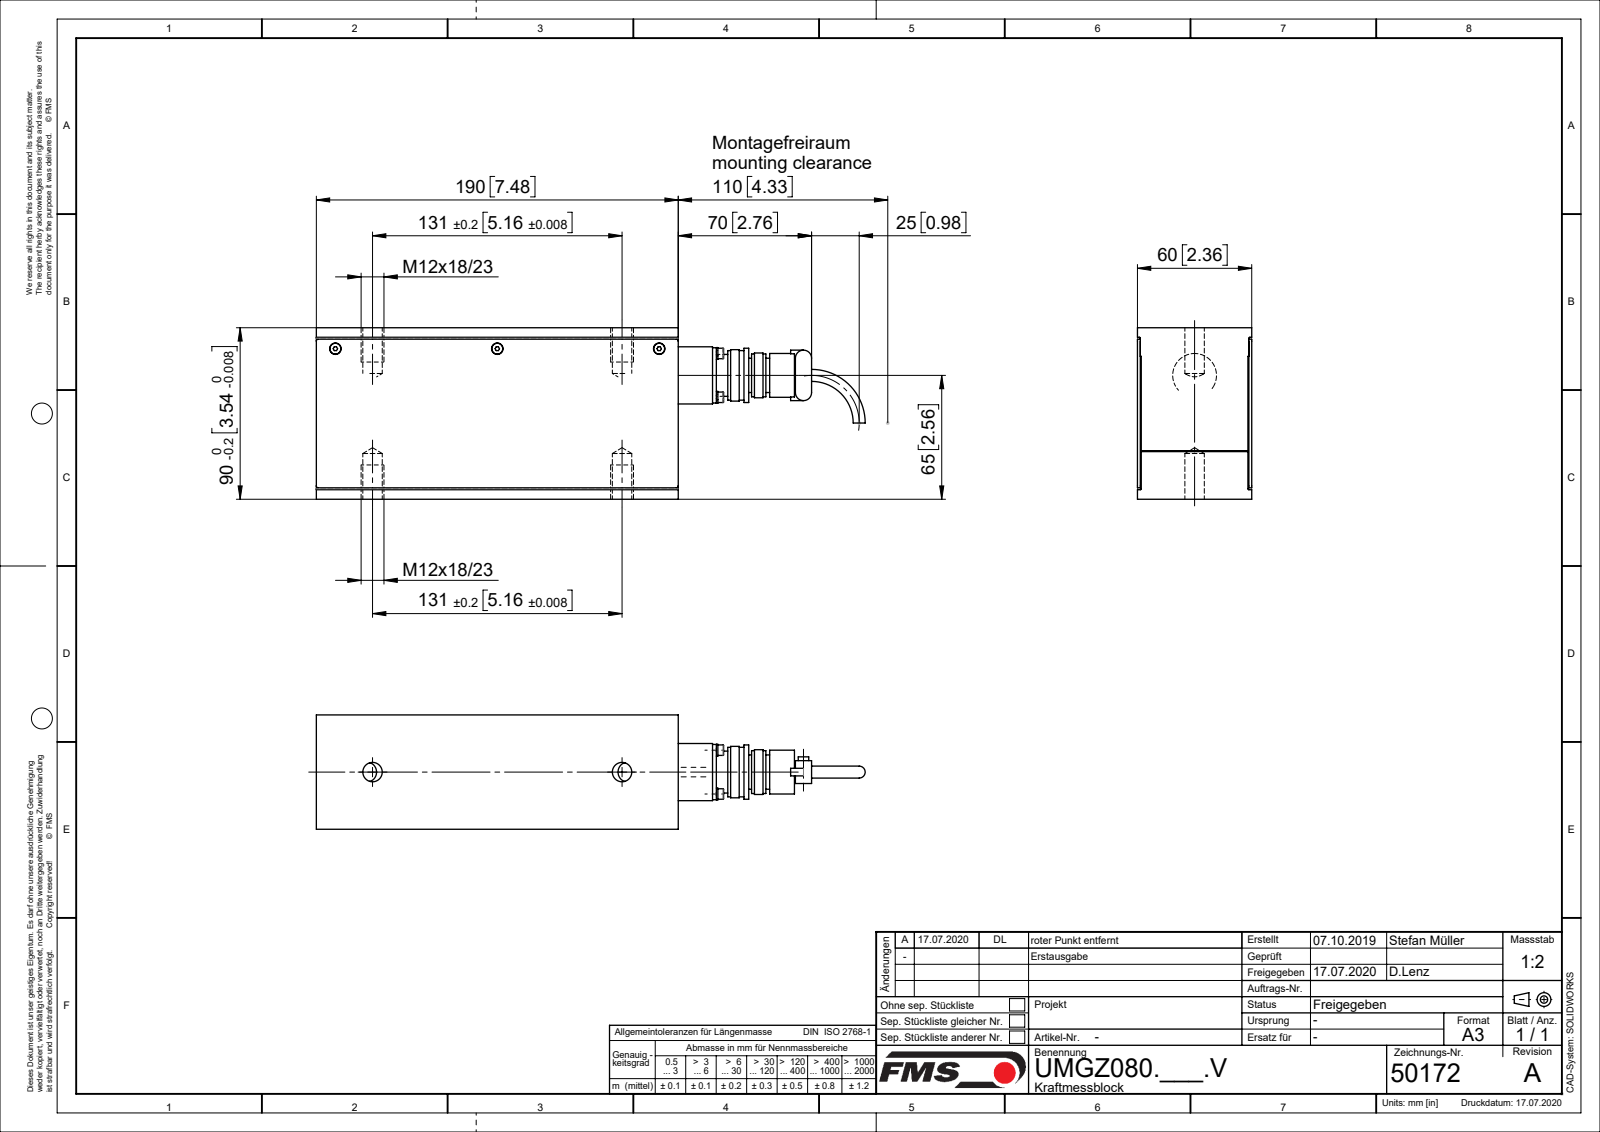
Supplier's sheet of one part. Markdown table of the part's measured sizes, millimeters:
| quantity | value |
| --- | --- |
| part name | U50172; U4957704; U49541; L49026 (+6 more) |
| STEP written by | Mechanical Desktop 2007 (CONFIG_CONTROL_DESIGN) |
| units | millimeters |
| bodies | 19 solids, 382 faces (134 planar, 162 cylindrical, 86 other) |
| overall size | 310.5 × 90 × 60 |
| volume | 1 041 000 mm³ |
| surface area | 151 386 mm² |
| round holes (diameter × count) | 2.6 × 7, 3.2 × 4, 3.4 × 4, 6 × 3, 10.68 × 2, 10.91 × 1, 23 × 1 |
| round bosses / shafts (diameter × count) | 3 × 7, 6.2 × 4, 5.5 × 4, 2.5 × 4, 28 × 1, 22 × 1, 21 × 1, 20 × 1 |
| partial cylindrical surfaces (radius × count) | 1 × 4, 4 × 4 |
| main face-to-face distances | 1.5, 58.5, 2, 58, 0.5, 56.5, 57, 60, 56, 90 |
| hole center spacings | 16.26, 23, 32.53, 85, 131, 170 |
